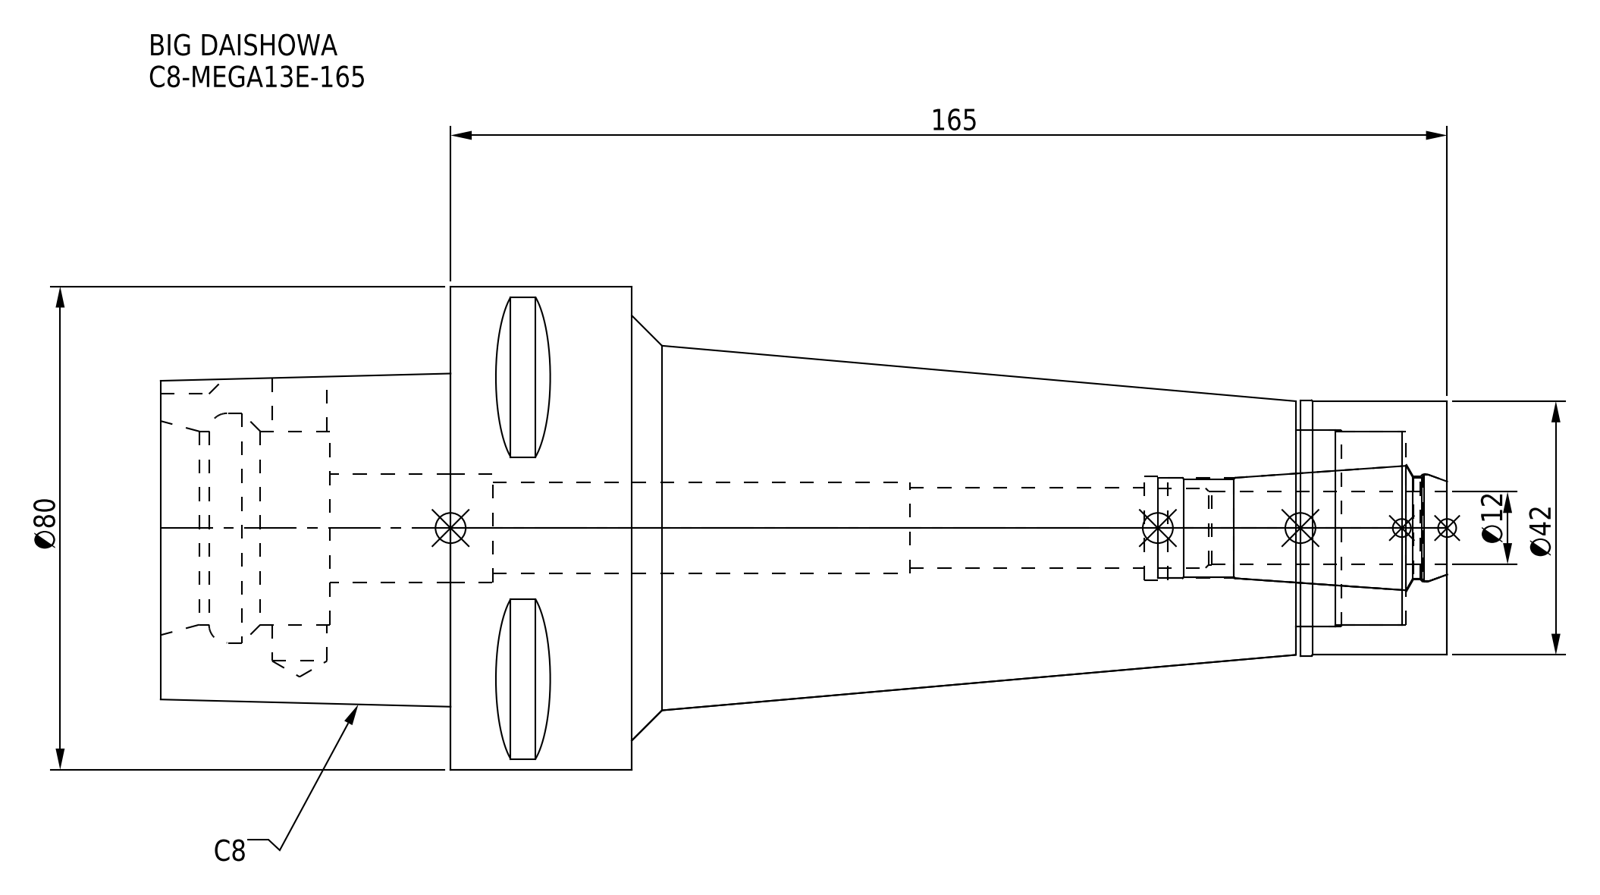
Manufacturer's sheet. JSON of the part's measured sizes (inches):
{"part_name": "C8-MEGA13E-165-120-FreeParts; C8-MEGA13E-165; C8-MEGA13E-165-120_ASM.stp; C8-MEGA13E-165-120.stp (+3 more)", "step_written_by": "SolidWorks 2019 (CONFIG_CONTROL_DESIGN)", "units": "inches", "bodies": {"solids": 2, "faces": 100, "planar": 37, "cylindrical": 39, "other": 24}, "overall_size": [8.386, 3.15, 3.15], "volume_in3": 28.18, "surface_area_in2": 98.14, "round_holes": [[0.358, 1], [0.524, 1], [0.591, 1], [0.654, 1], [0.669, 1], [0.677, 1], [0.705, 1], [0.709, 1], [1.26, 1], [1.28, 1], [1.496, 1]], "round_bosses_or_shafts": [[3.15, 1], [1.665, 1], [1.654, 1]], "partial_cylinders_radius": [[0.236, 1]], "face_to_face_distances": [6.496, 5.315, 1.181, 8.386, 3.071, 1.89, 0.988, 0.957, 4.358, 5.539]}
